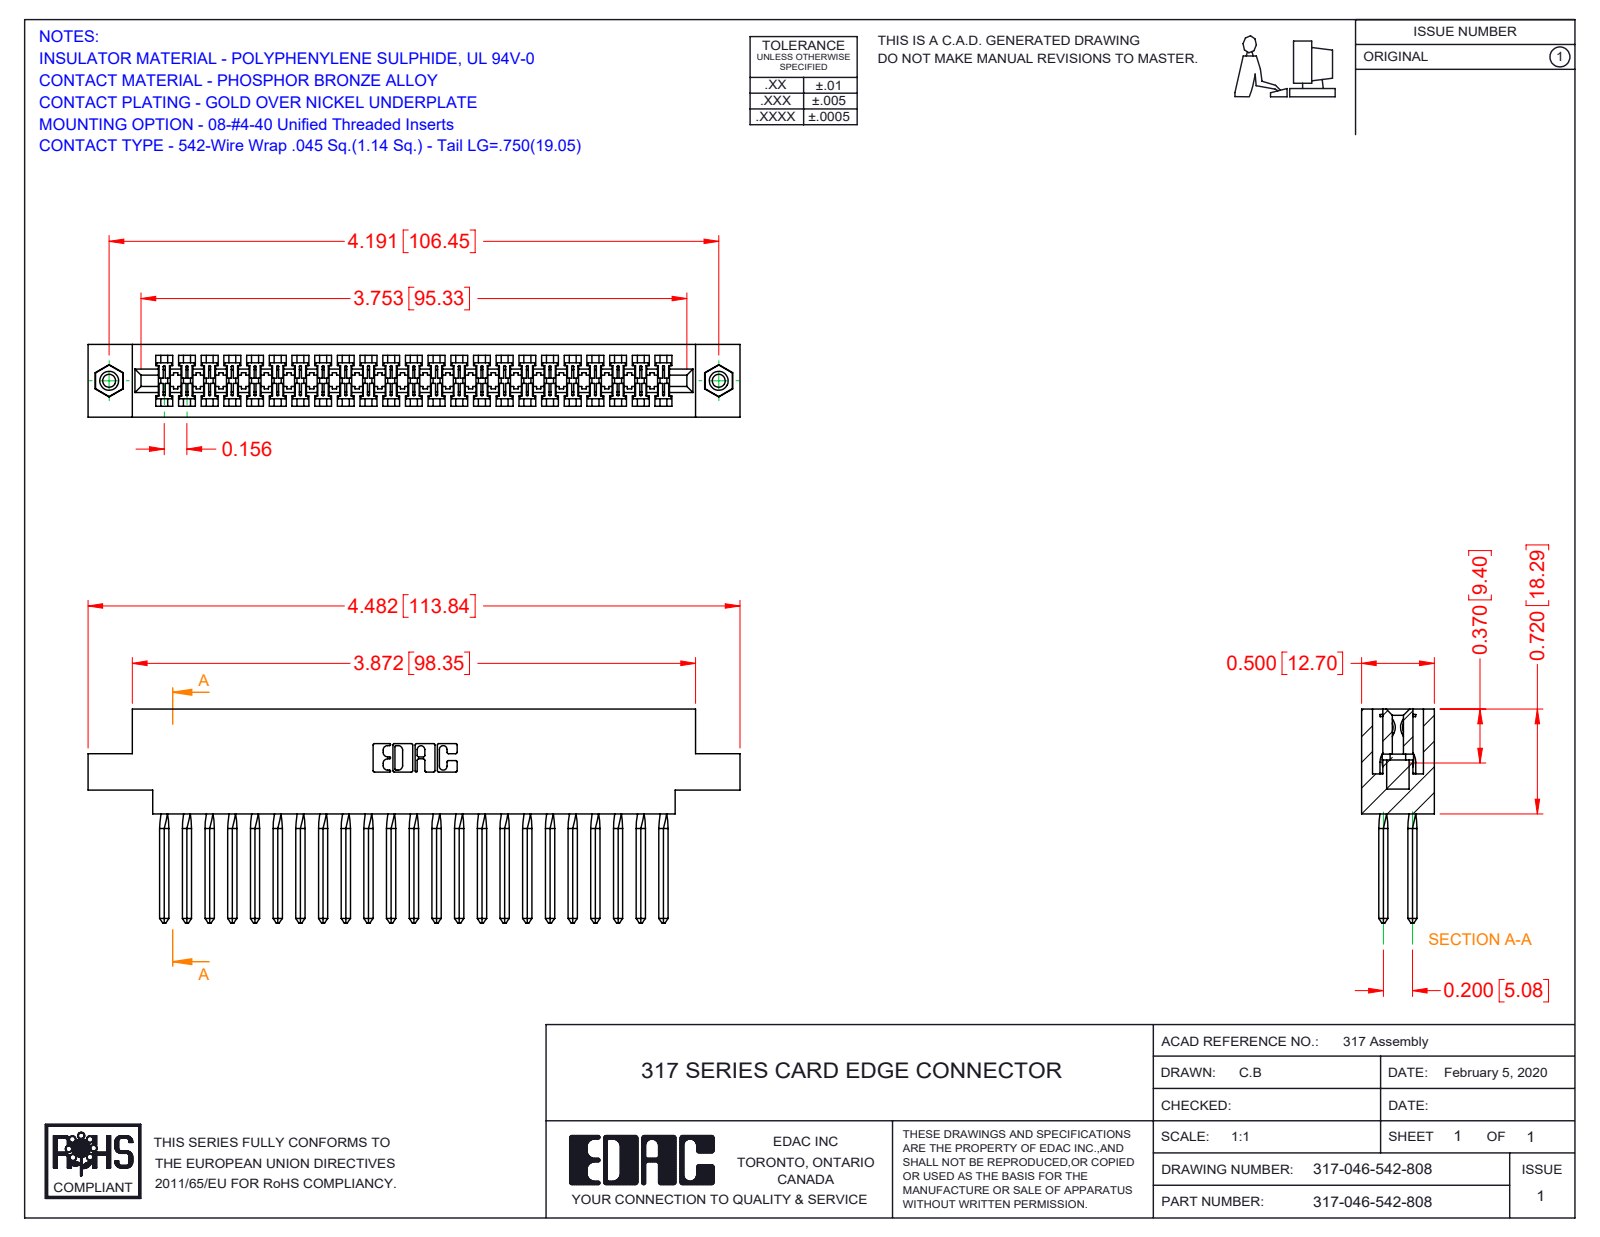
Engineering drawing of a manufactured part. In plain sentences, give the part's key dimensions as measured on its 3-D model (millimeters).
The part is named "317-046-542-878; 317 Part_.156 Dia - TI; 317-290-003_542; 345-250-001_345-250-003-102". Its 3-D file was written by "SolidWorks 2016 (CONFIG_CONTROL_DESIGN)". It is 49 solids with 2784 faces: 2206 planar, 378 cylindrical and 200 other. Overall it measures 113.8 by 37.3 by 12.7 millimeters. Its volume is 18 040 cubic millimeters and its surface area 24 490 square millimeters. Round holes: 2 of diameter 2.3, 2 of diameter 3.2, 2 of diameter 4. Round bosses or shafts: 2 of diameter 3.9. Partial cylindrical surfaces (rounded edges, fillets, slot ends): 92 of radius 0.2, 22 of radius 0.3, 6 of radius 0.2, 6 of radius 0.8, 3 of radius 0.7, 2 of radius 1.9, 2 of radius 2.3, 2 of radius 2.5. The main face-to-face distances are 12.7, 1.9, 10.8, 8.9, 2.8, 5.1, 2.9, 3.5, 1.2, 18.3. The hole center spacings are 106.5.
